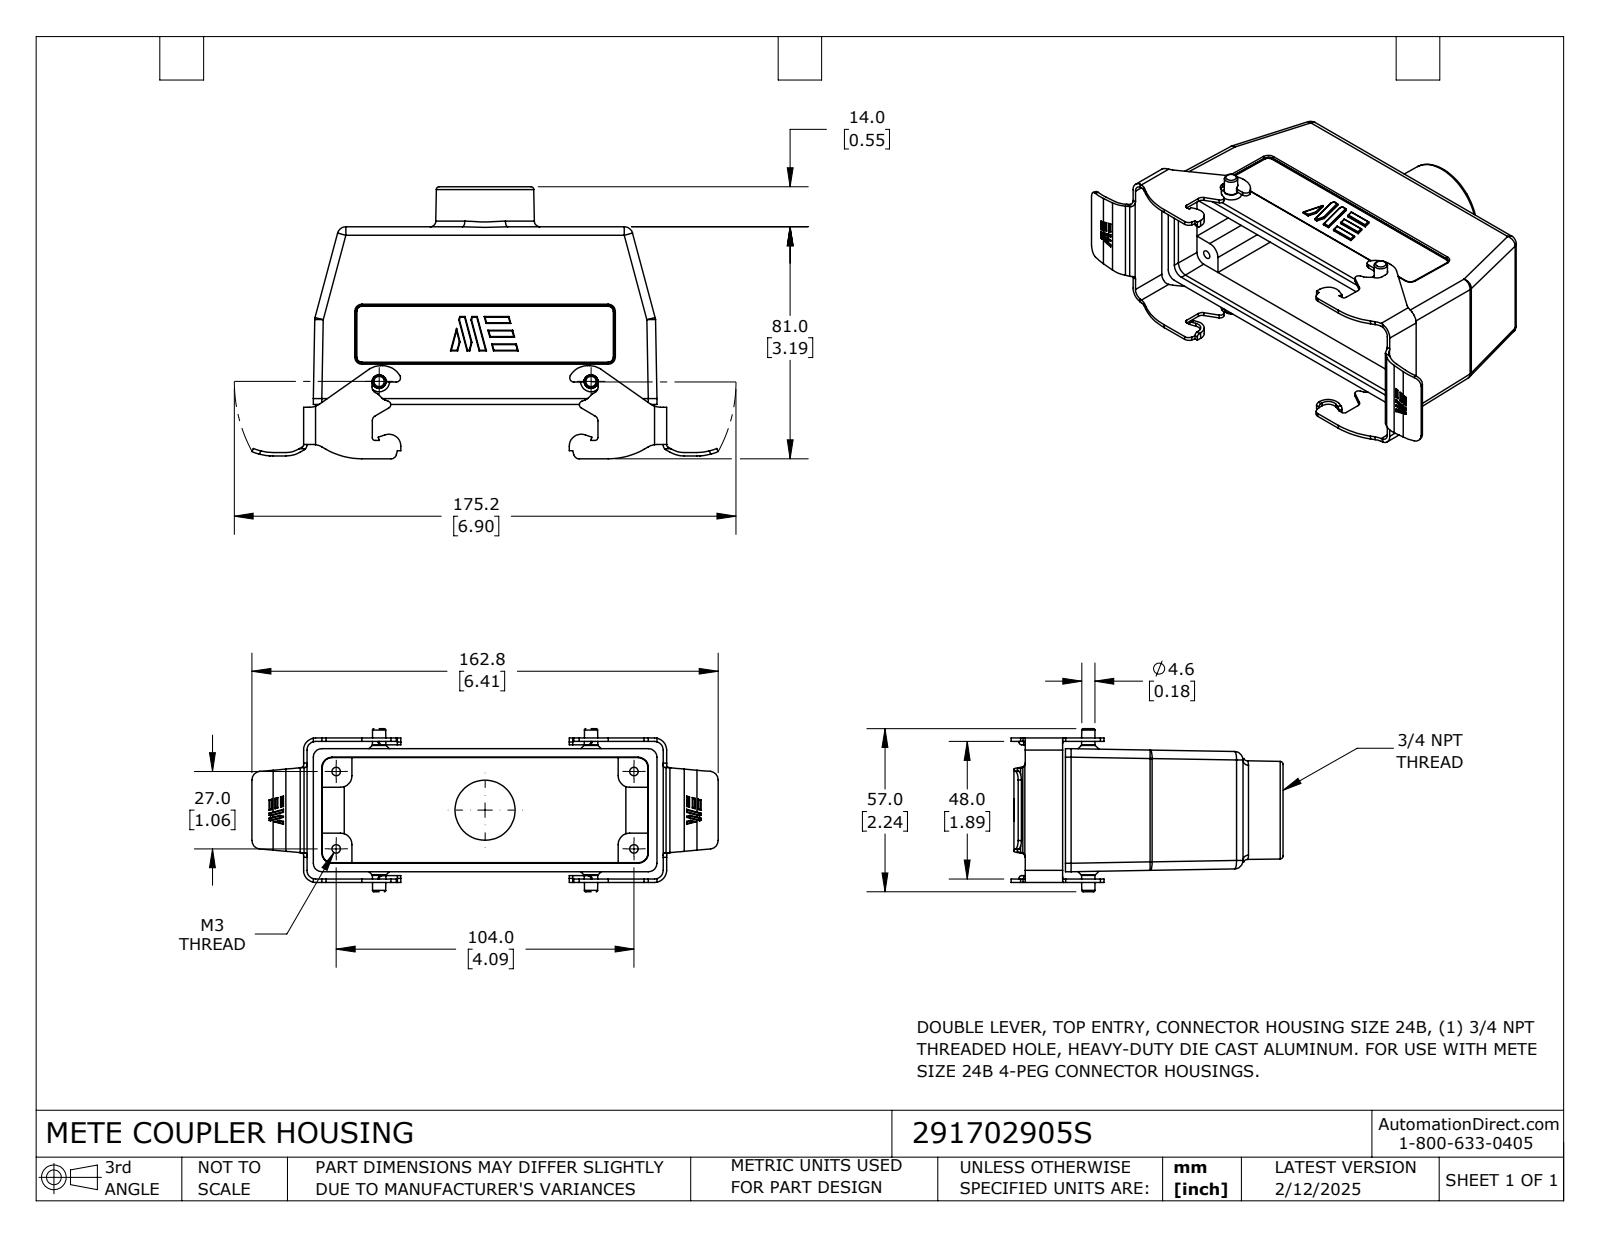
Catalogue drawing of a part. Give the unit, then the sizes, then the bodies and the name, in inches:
Units: inches
Overall size (bounding box): 6.409 × 3.74 × 2.244
Round holes (diameter × count): ⌀0.118 ×4, ⌀0.827 ×1, ⌀1.063 ×1
Partial cylindrical surfaces — rounded edges, fillets, slot ends (radius × count): R0.008 ×86, R0.118 ×22, R0.039 ×18, R0.079 ×14, R0.02 ×10, R0.031 ×6, R0.059 ×6, R0.098 ×6
Main face-to-face distances: 1.444, 0.118, 0.047, 0.031, 0.27, 1.714, 1.937, 0.223, 1.667, 0.197
Hole centre spacings: 2.115, 1.063, 4.094, 4.23
Volume: 5.423 in³ · Surface area: 90.94 in²
Bodies: 1 solid, 661 faces (256 planar, 290 cylindrical, 115 other)
Part name (STEP PRODUCT): 291702905S
STEP written by: SolidWorks 2024 (CONFIG_CONTROL_DESIGN)
